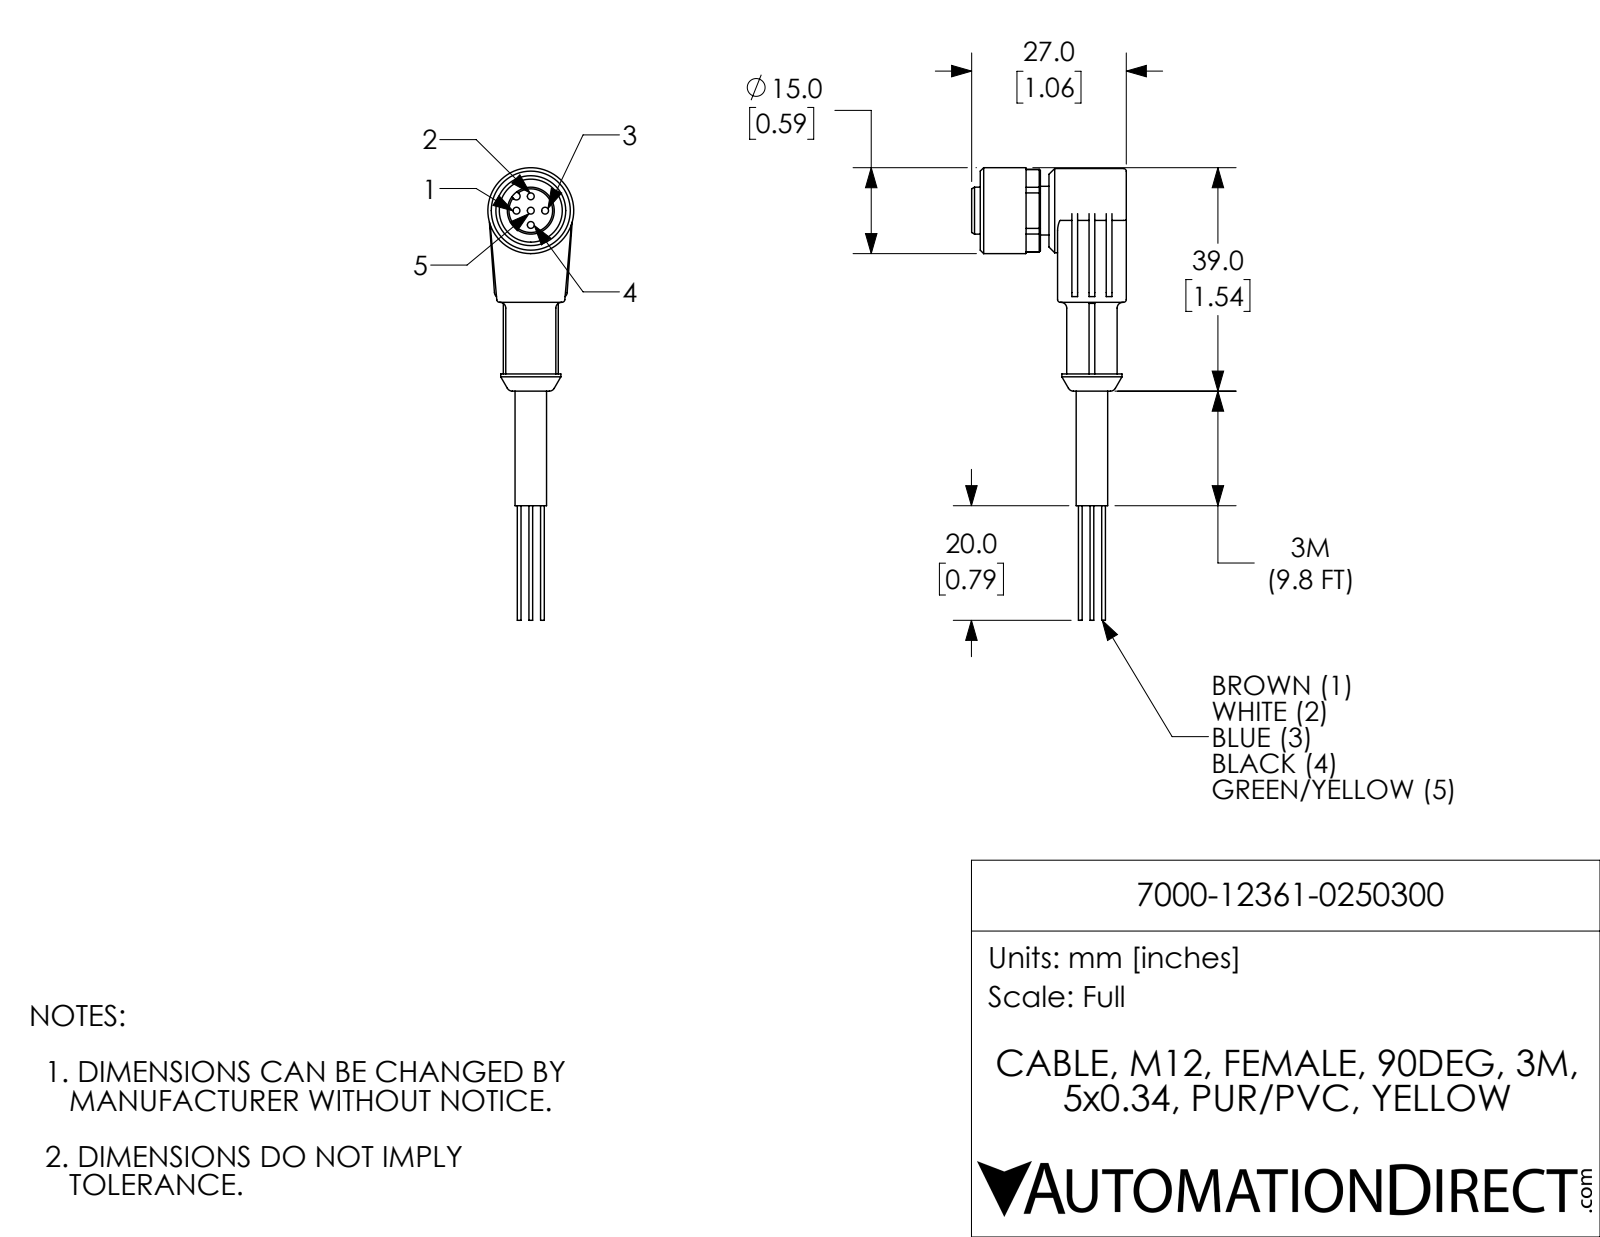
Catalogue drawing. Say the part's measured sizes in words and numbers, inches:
The part is named "7000-12361-0250300". Its 3-D file was written by "SolidWorks 2017 (AUTOMOTIVE_DESIGN)". It is 1 solid with 155 faces: 66 planar, 61 cylindrical and 28 other. Overall it measures 3.11 by 1.063 by 0.591 inches. Its volume is 0.417 cubic inches and its surface area 5.916 square inches. Round holes: 5 of diameter 0.047, 1 of diameter 0.189, 1 of diameter 0.433. Round bosses or shafts: 5 of diameter 0.026, 1 of diameter 0.591, 1 of diameter 0.579, 1 of diameter 0.413, 1 of diameter 0.346, 1 of diameter 0.335, 1 of diameter 0.323, 1 of diameter 0.217. Partial cylindrical surfaces (rounded edges, fillets, slot ends): 8 of radius 0.02, 2 of radius 0.039, 1 of radius 0.026, 1 of radius 0.283. The main face-to-face distances are 0.472, 0.059, 0.118, 0.531, 0.591, 0.217, 0.374, 0.236, 0.315, 0.492. The hole center spacings are 0.098, 0.139, 0.197.
